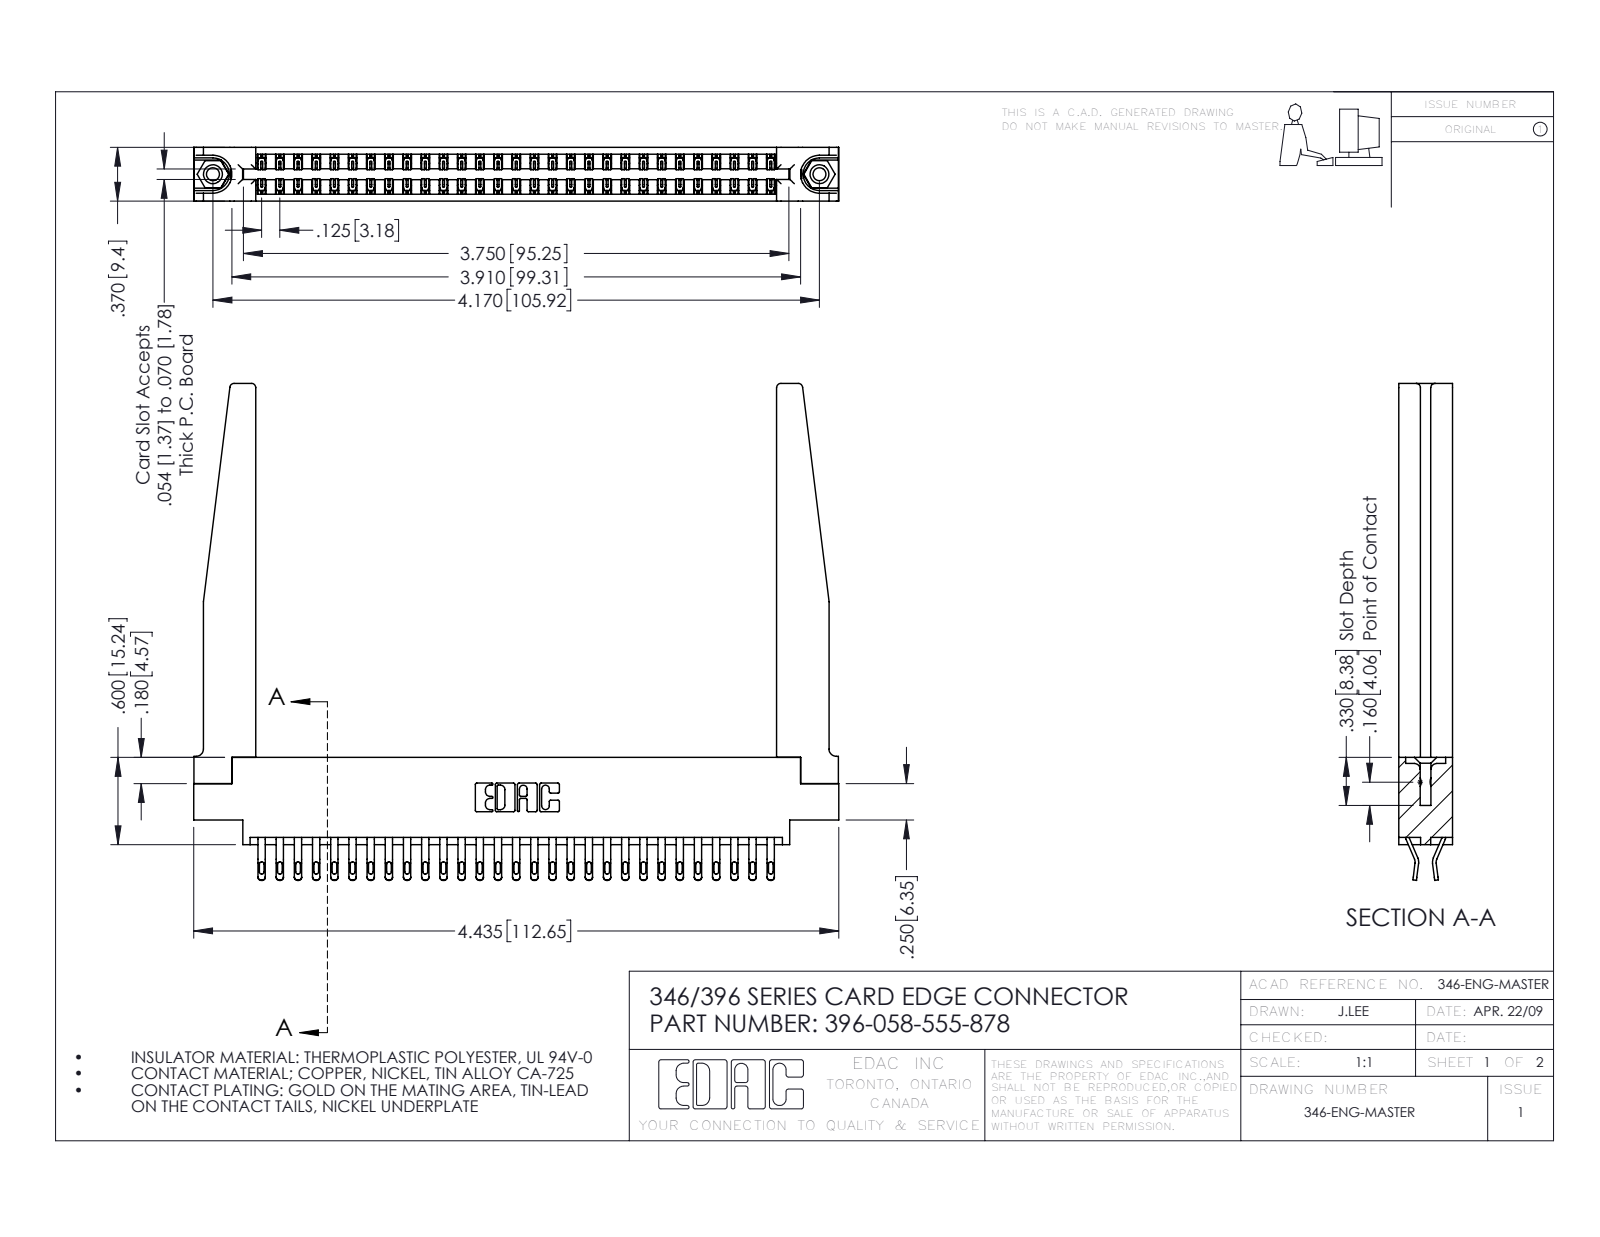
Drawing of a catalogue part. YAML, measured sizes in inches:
part_name: "396-058-555-878; 345-250-001_345-250-001-102; 346-220-078_345-220-078; 345-292-001_555 Tail (+1 more)"
step_written_by: "SolidWorks 2016 (CONFIG_CONTROL_DESIGN)"
units: inches
bodies: {solids: 63, faces: 3724, planar: 2136, cylindrical: 1536, other: 52}
overall_size: [4.435, 3.415, 0.37]
volume: 1.087
surface_area: 34.24
round_holes:
  - {diameter: 0.089, count: 2}
  - {diameter: 0.125, count: 2}
  - {diameter: 0.156, count: 2}
  - {diameter: 0.064, count: 1}
round_bosses_or_shafts:
  - {diameter: 0.155, count: 2}
partial_cylinders:
  - {radius: 0.016, count: 116}
  - {radius: 0.02, count: 116}
  - {radius: 0.006, count: 87}
  - {radius: 0.01, count: 22}
  - {radius: 0.03, count: 8}
  - {radius: 0.007, count: 6}
  - {radius: 0.031, count: 6}
  - {radius: 0.05, count: 4}
face_to_face_distances: [0.37, 0.048, 0.322, 0.072, 0.15, 0.148, 0.25, 0.025, 0.298, 0.275]
hole_center_spacings: [0.246, 3.962, 4.17]
